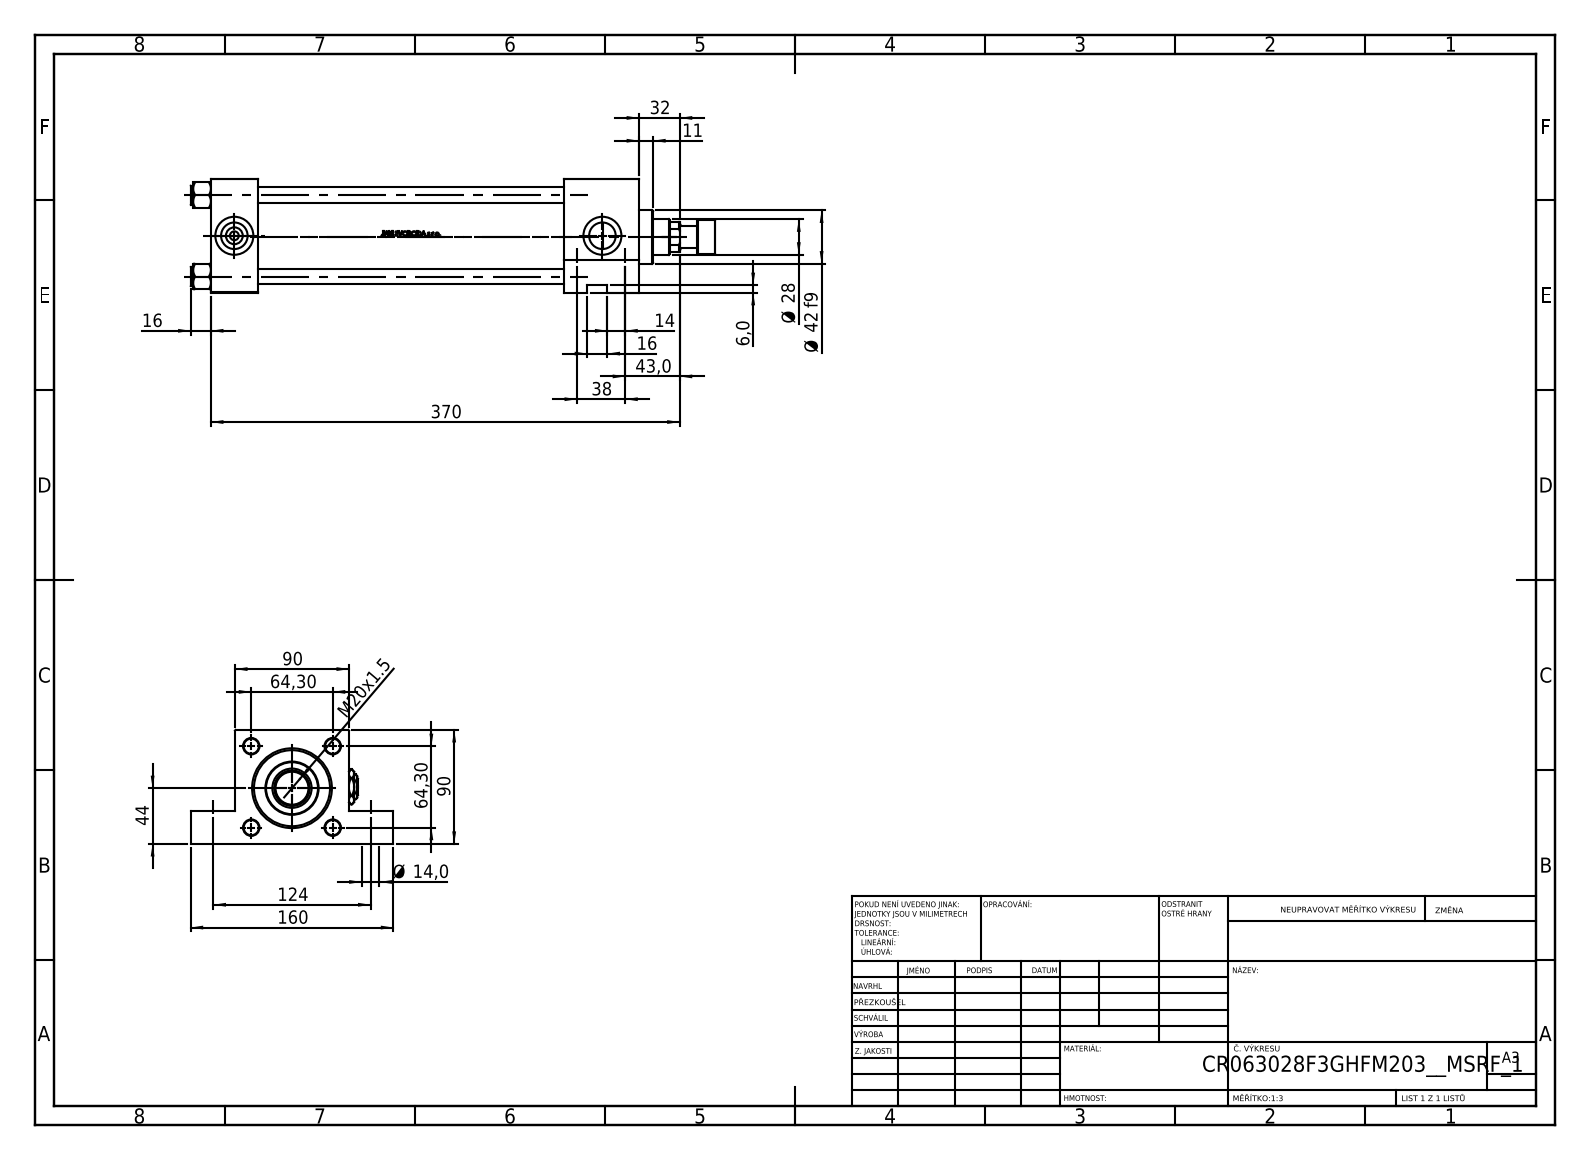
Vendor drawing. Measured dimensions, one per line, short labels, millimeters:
name: NUT_M5_F; V215_VC_A; V215CR_ROD_END_F; V215CR_F_Body (+3 more)
written by: SolidWorks 2019 (CONFIG_CONTROL_DESIGN)
unit: mm
bodies: 14 solids, 1214 faces (488 planar, 138 cylindrical, 588 other)
size: 414 × 160 × 90
volume: 1 344 000 mm³; area: 321 496 mm²
holes: 4× ⌀12, 4× ⌀14, 3× ⌀20.96, 3× ⌀30, 2× ⌀7, 1× ⌀18.5, 1× ⌀20, 1× ⌀28, 1× ⌀31, 1× ⌀50, 1× ⌀60, 1× ⌀63
bosses: 4× ⌀15, 1× ⌀69, 1× ⌀42, 1× ⌀27, 1× ⌀18
face distances: 90, 37, 301, 338, 279, 242, 59, 26, 64, 35
hole spacings: 64.3, 38, 44.77, 46.18, 90.93, 124, 129.69, 10
